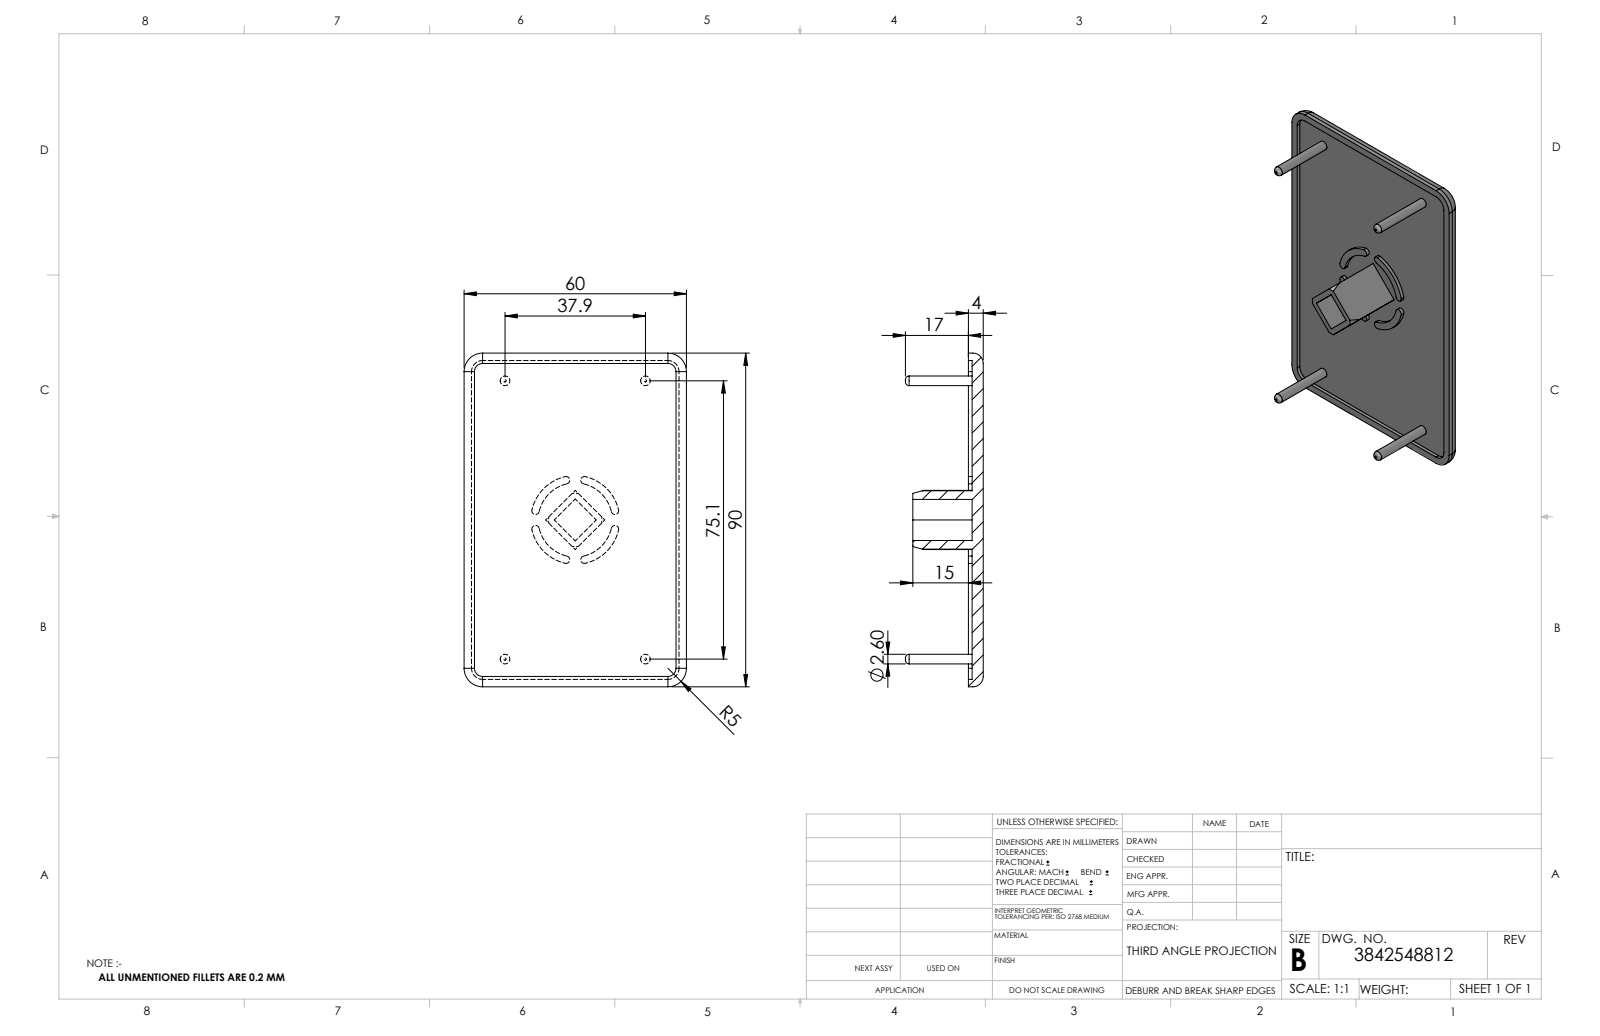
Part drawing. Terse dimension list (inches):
name: 3842548812
written by: SolidWorks 2014 (CONFIG_CONTROL_DESIGN)
unit: in
bodies: 1 solid, 85 faces (33 planar, 40 cylindrical, 12 other)
size: 3.543 × 2.362 × 0.827
volume: 1.081 in³; area: 21.35 in²
bosses: 4× ⌀0.102
rounds: 8× R0.039, 4× R0.11, 4× R0.118, 4× R0.197, 1× R0.394, 1× R0.472
face distances: 0.118, 0.039, 0.157, 0.065, 0.38, 0.444, 0.079, 0.315, 2.283, 3.465
